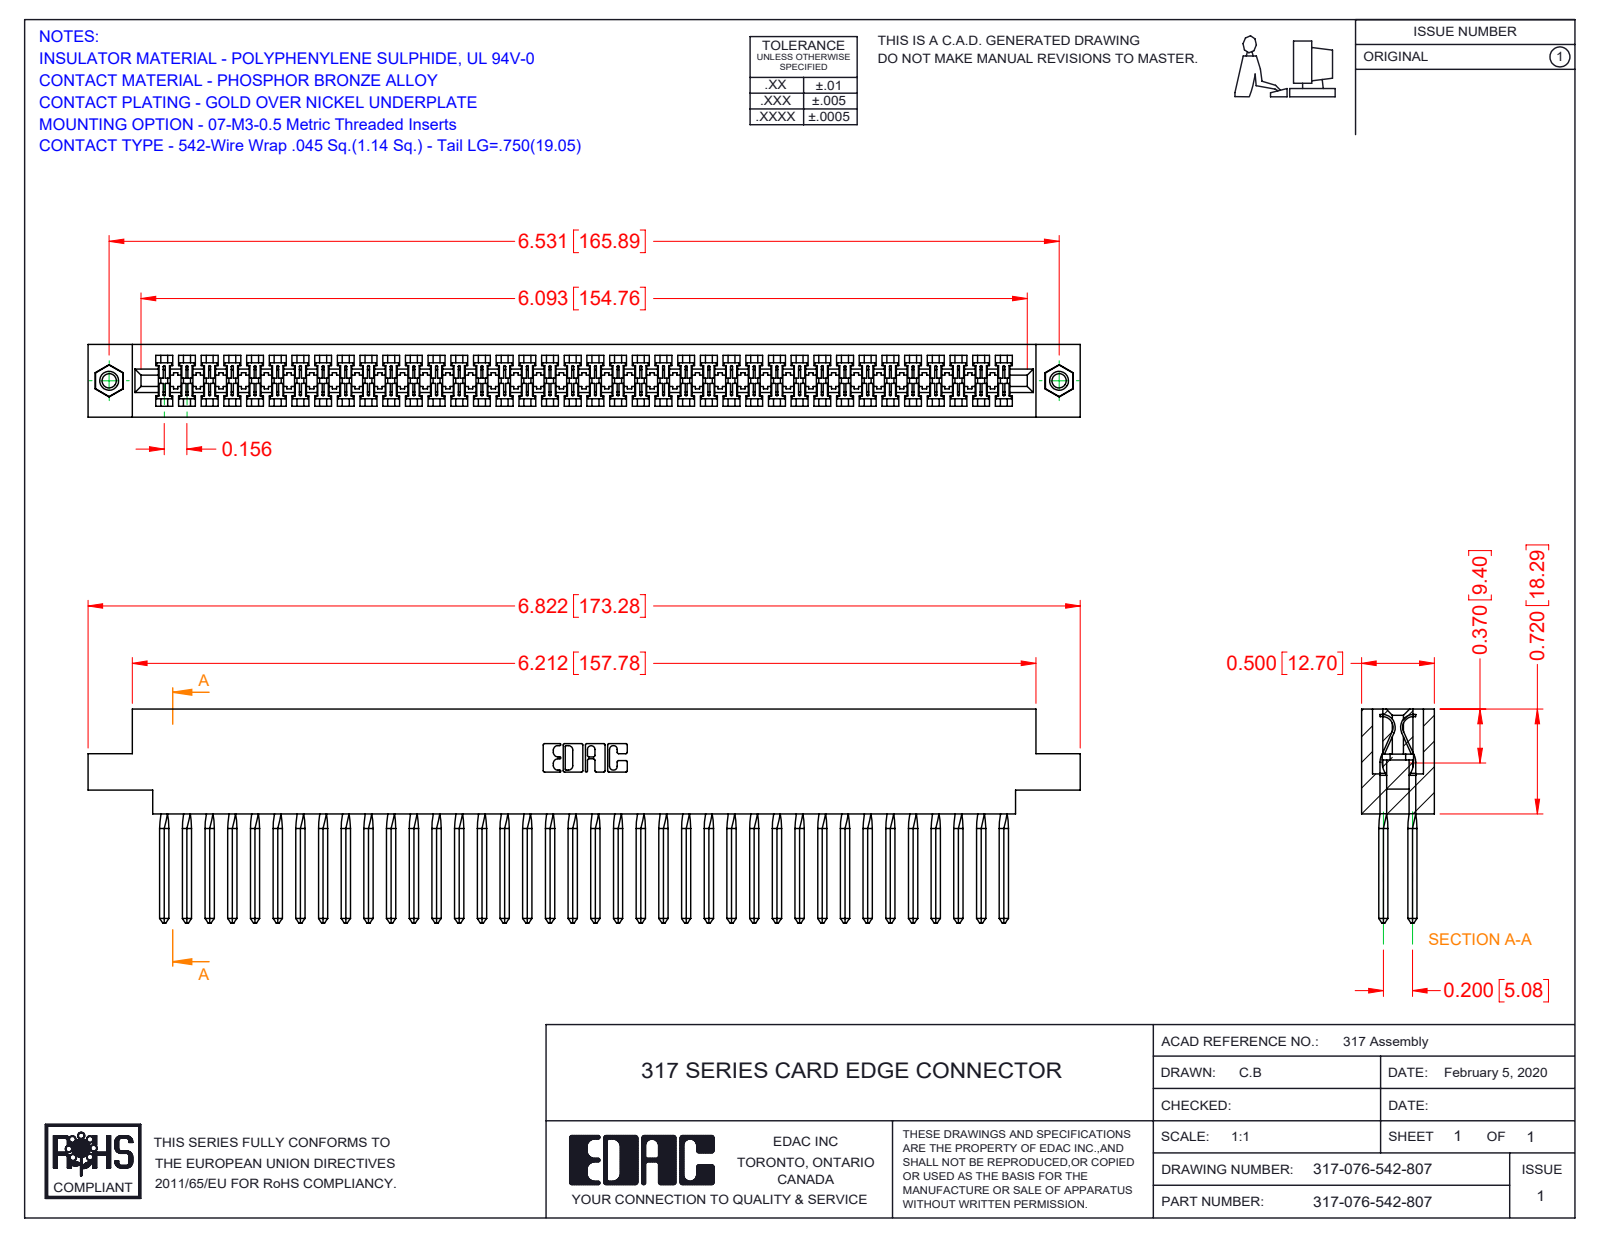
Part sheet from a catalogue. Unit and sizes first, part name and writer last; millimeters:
Units: millimetres
Overall size (bounding box): 173.3 × 37.3 × 12.7
Round holes (diameter × count): ⌀2.5 ×2, ⌀3.2 ×2, ⌀4 ×2
Round bosses / shafts (diameter × count): ⌀3.9 ×2
Partial cylindrical surfaces — rounded edges, fillets, slot ends (radius × count): R0.2 ×152, R0.3 ×22, R0.2 ×6, R0.8 ×6, R0.7 ×3, R1.9 ×2, R2.3 ×2, R2.5 ×2
Main face-to-face distances: 12.7, 1.9, 10.8, 8.9, 5.1, 1.2, 3.3, 9.4, 1.3, 7.5
Hole centre spacings: 165.9
Volume: 28 230 mm³ · Surface area: 39 170 mm²
Bodies: 79 solids, 4494 faces (3586 planar, 588 cylindrical, 320 other)
Part name (STEP PRODUCT): 345-250-001_345-250-005-103; 317 Part_.156 Dia - TI; 317-290-003_542; 317-076-542-807
STEP written by: SolidWorks 2016 (CONFIG_CONTROL_DESIGN)
